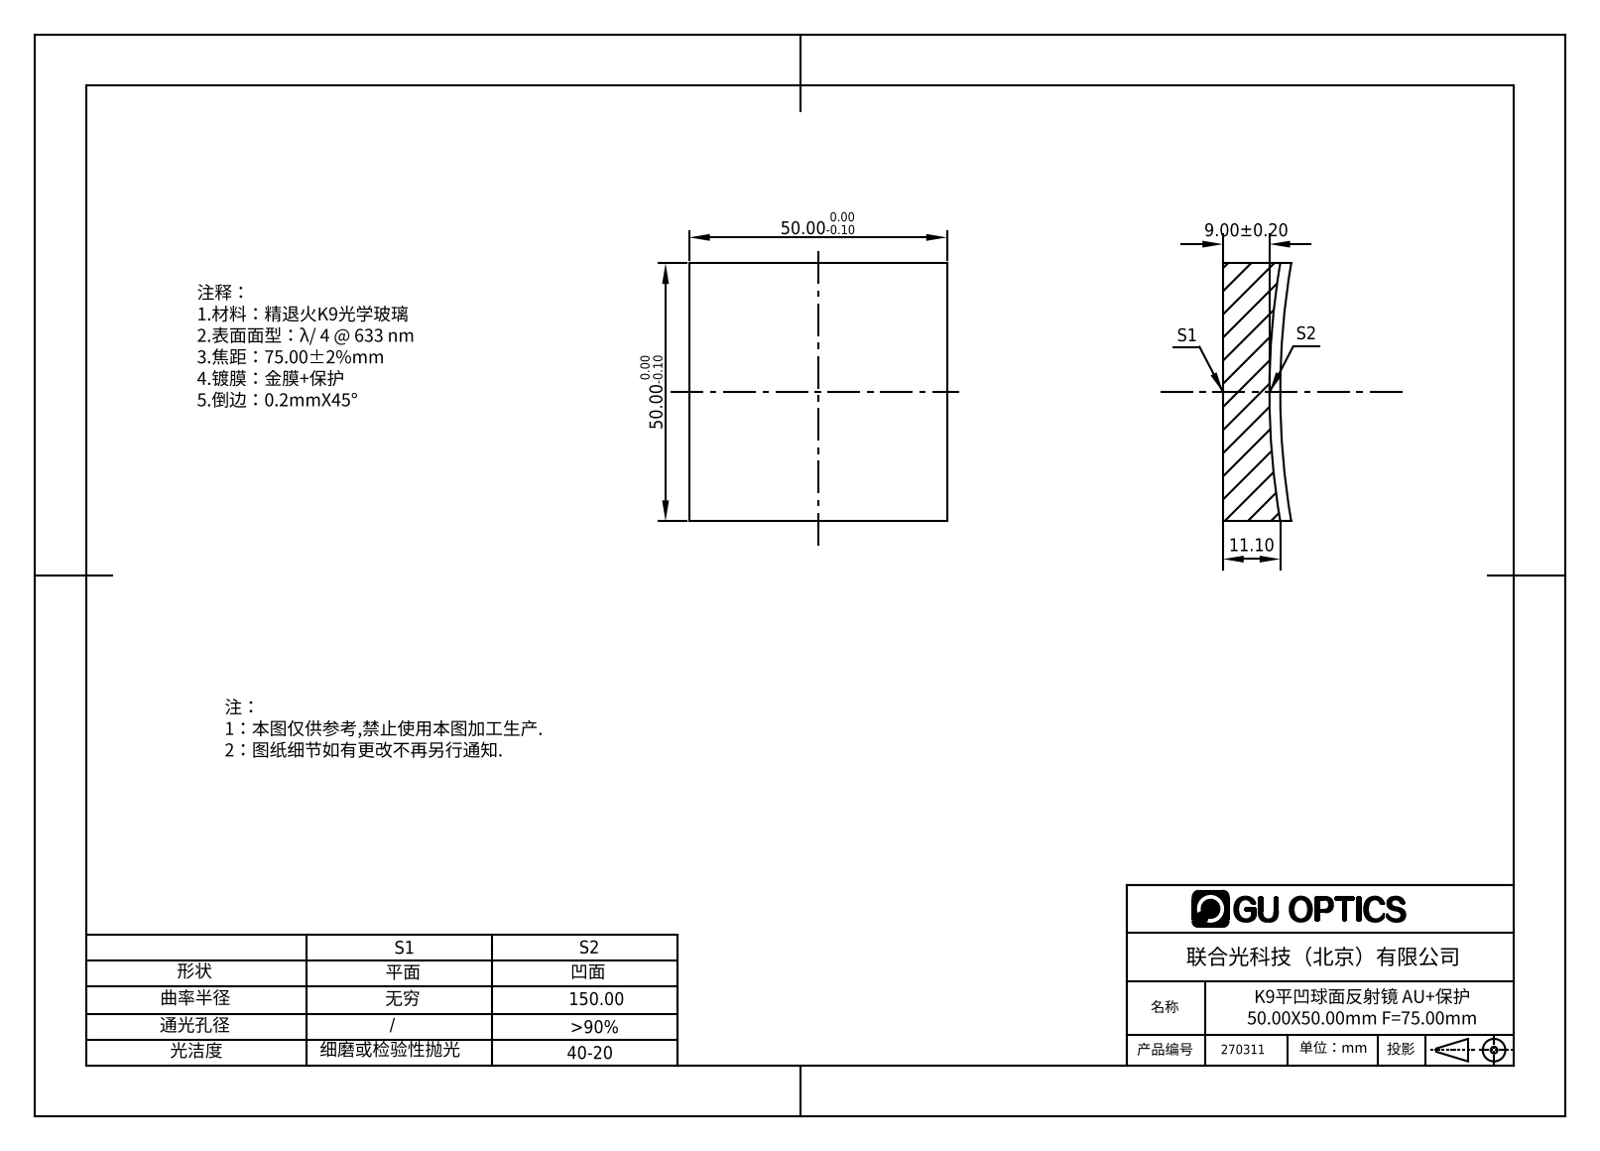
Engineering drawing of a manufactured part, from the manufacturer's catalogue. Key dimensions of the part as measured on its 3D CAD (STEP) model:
Part name (STEP PRODUCT): 270051
STEP written by: SolidWorks 2019 (AUTOMOTIVE_DESIGN)
Units: millimetres
Bodies: 1 solid, 7 faces (5 planar, 0 cylindrical, 2 other)
Overall size (bounding box): 50 × 50 × 13.23
Volume: 25 995 mm³ · Surface area: 7 385 mm²
Main face-to-face distances: 50
